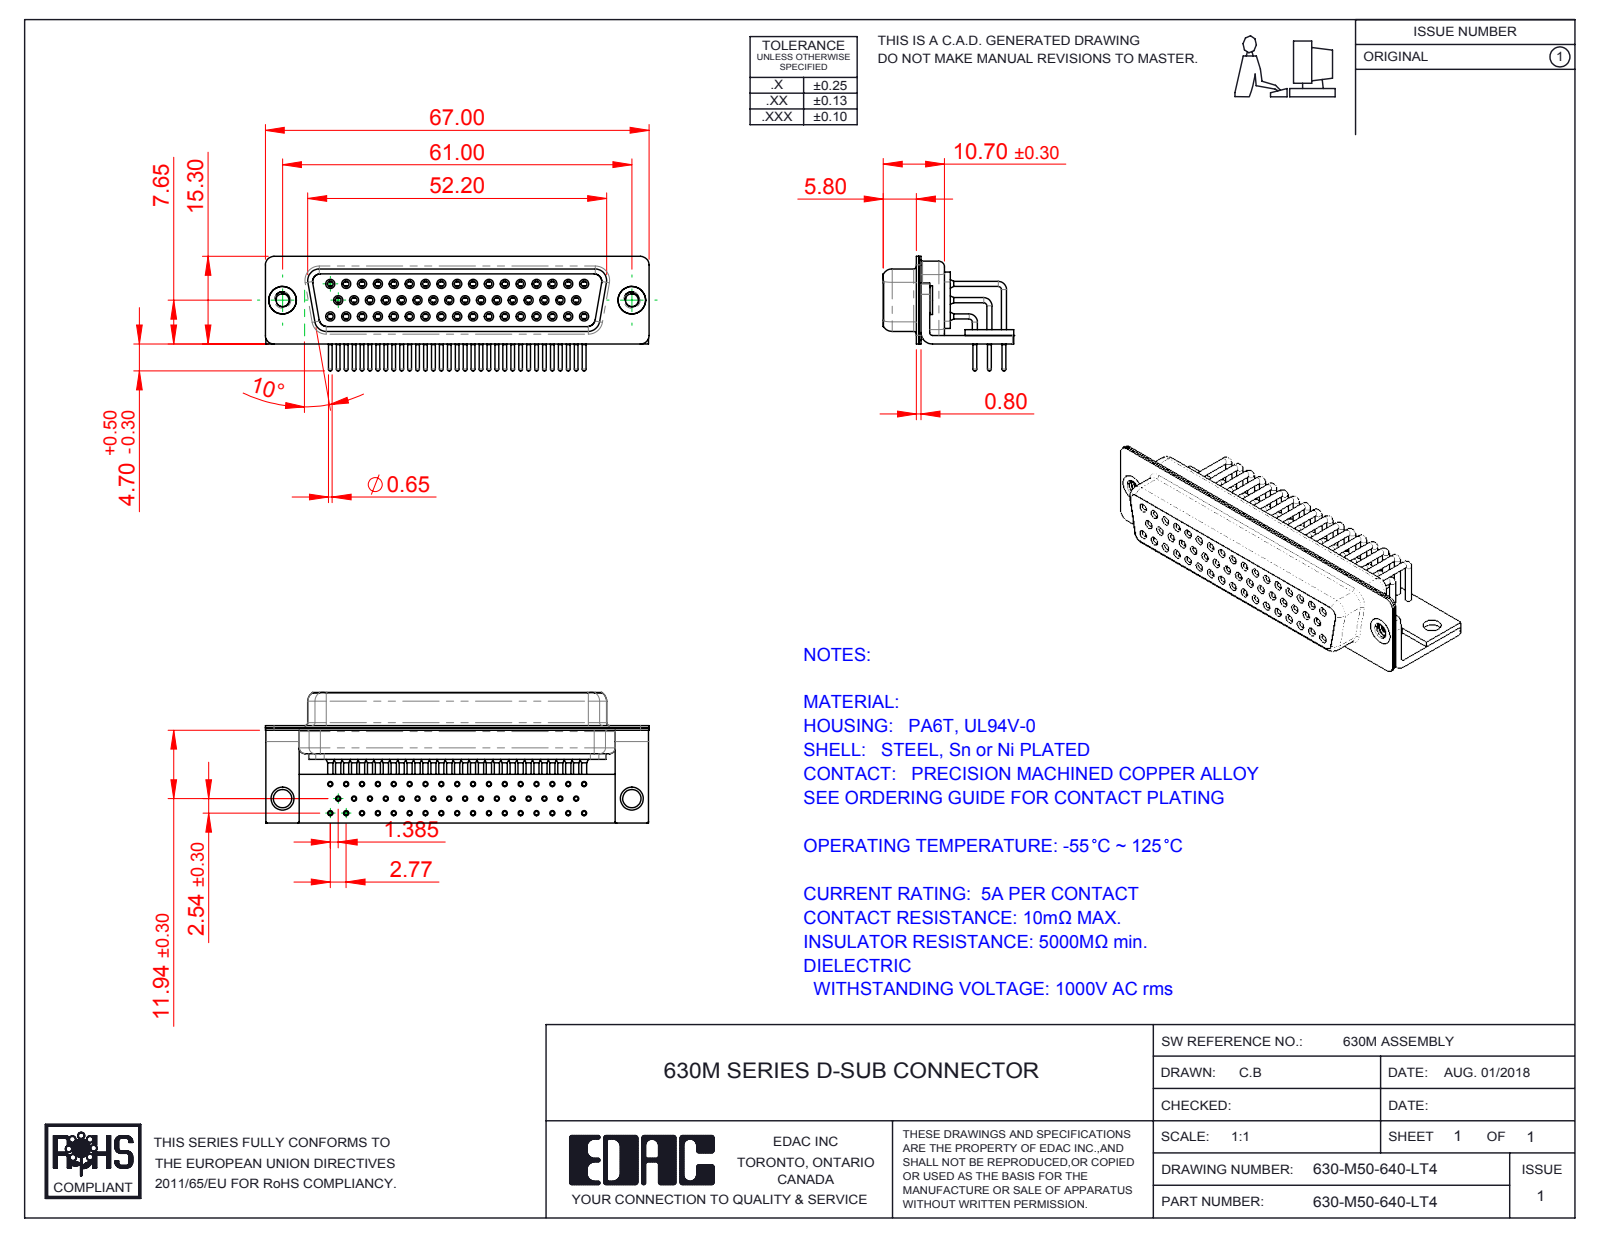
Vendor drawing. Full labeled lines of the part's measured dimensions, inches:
Part name (STEP PRODUCT): 630M Shell Front_50 Contacts; 630M Housing_50 Contacts; 630-M50-640-LT4; 630M Stabilizer Board_50 Contacts (+6 more)
STEP written by: SolidWorks 2016 (CONFIG_CONTROL_DESIGN)
Units: inches
Bodies: 58 solids, 3079 faces (843 planar, 1409 cylindrical, 827 other)
Overall size (bounding box): 2.638 × 0.898 × 0.787
Volume: 0.48 in³ · Surface area: 28.83 in²
Round holes (diameter × count): ⌀0.035 ×50, ⌀0.039 ×50, ⌀0.043 ×50, ⌀0.067 ×50, ⌀0.071 ×50, ⌀0.079 ×50, ⌀0.089 ×2, ⌀0.126 ×2, ⌀0.157 ×2, ⌀0.189 ×2
Round bosses / shafts (diameter × count): ⌀0.035 ×59, ⌀0.063 ×50, ⌀0.059 ×50, ⌀0.026 ×50, ⌀0.197 ×2, ⌀0.193 ×2
Partial cylindrical surfaces — rounded edges, fillets, slot ends (radius × count): R0.01 ×16, R0.059 ×16, R0.079 ×13, R0.053 ×8, R0.063 ×8, R0.02 ×5, R0.024 ×4, R0.026 ×4
Main face-to-face distances: 0.016, 0.039, 0.087, 0.033, 0.053, 0.467, 0.482, 0.228, 0.232, 0.031
Hole centre spacings: 0.109, 0.218, 0.327, 0.436, 0.545, 0.654, 0.124, 0.763
